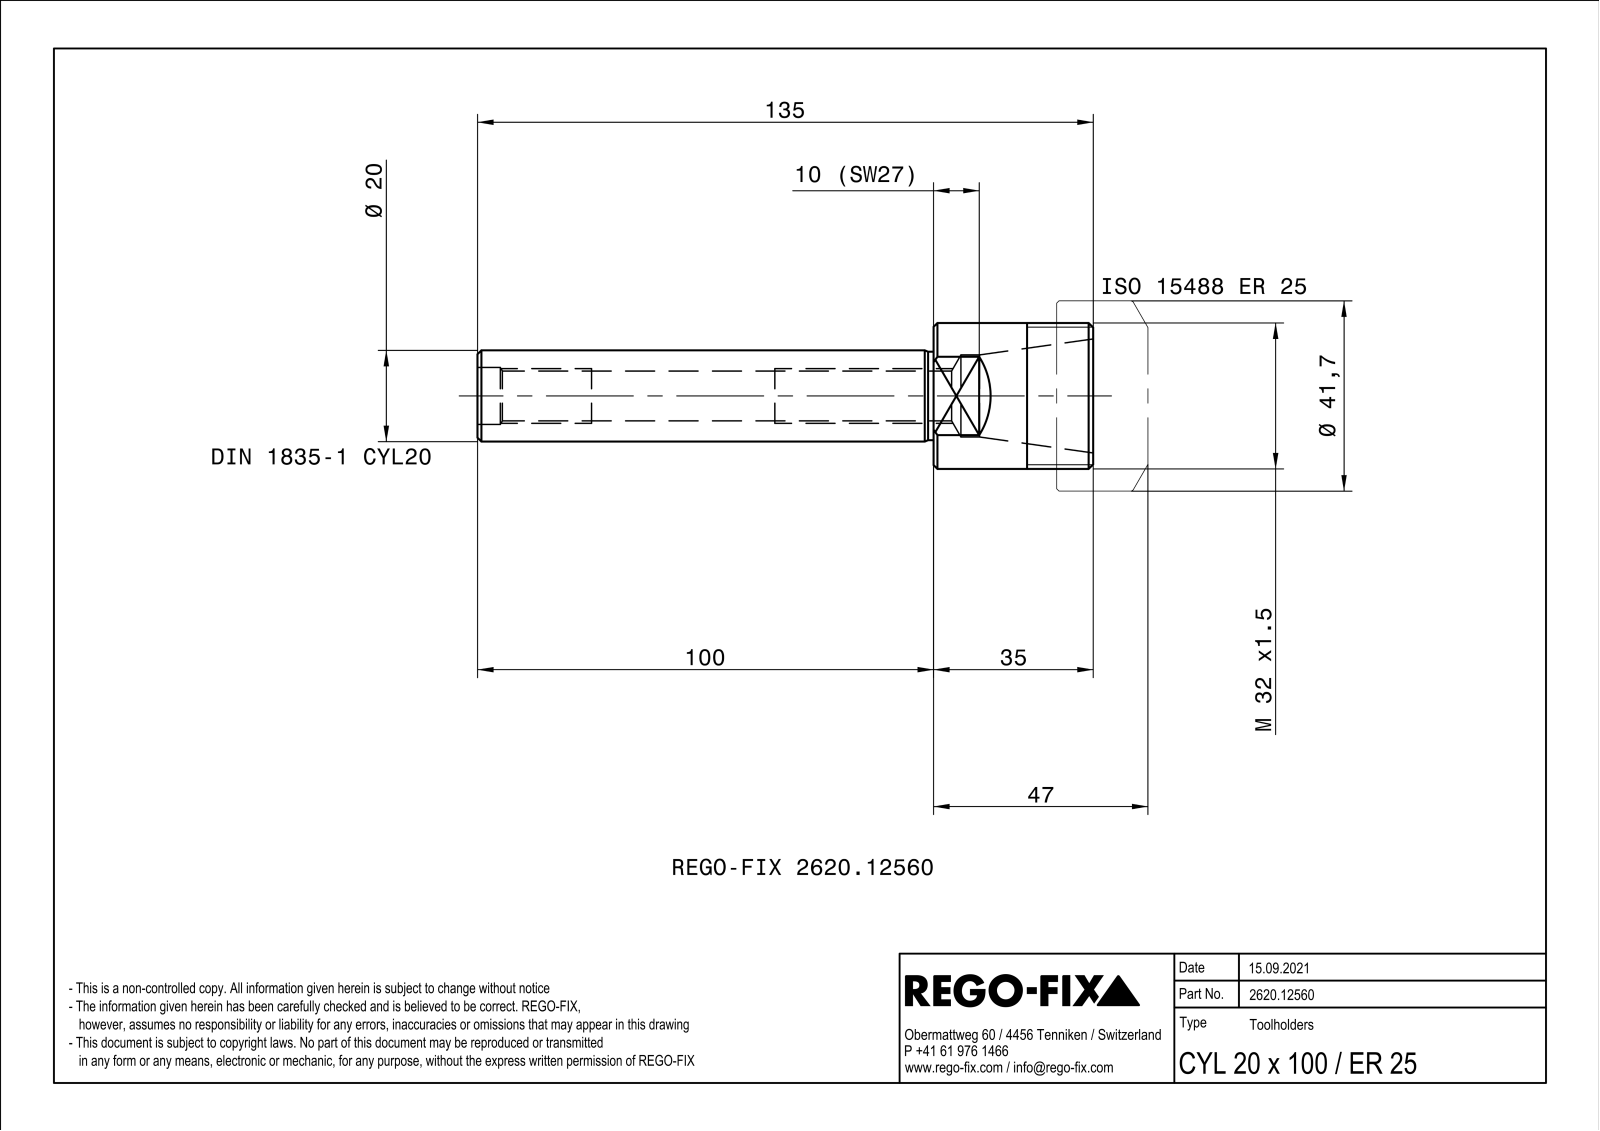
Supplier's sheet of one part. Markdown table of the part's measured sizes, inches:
| quantity | value |
| --- | --- |
| part name | NOCUT |
| STEP written by | SIEMENS PLM Software Solid Edge ST10 (AUTOMOTIVE_DESIGN) |
| units | inches |
| bodies | 1 solid, 29 faces (9 planar, 9 cylindrical, 11 other) |
| overall size | 5.315 × 1.26 × 1.26 |
| volume | 2.344 in³ |
| surface area | 25.24 in² |
| round holes (diameter × count) | 0.43 × 1, 0.492 × 1, 0.709 × 1 |
| round bosses / shafts (diameter × count) | 1.26 × 1, 0.787 × 1, 0.772 × 1 |
| main face-to-face distances | 1.378, 1.063, 5.315, 3.937, 0.255 |
